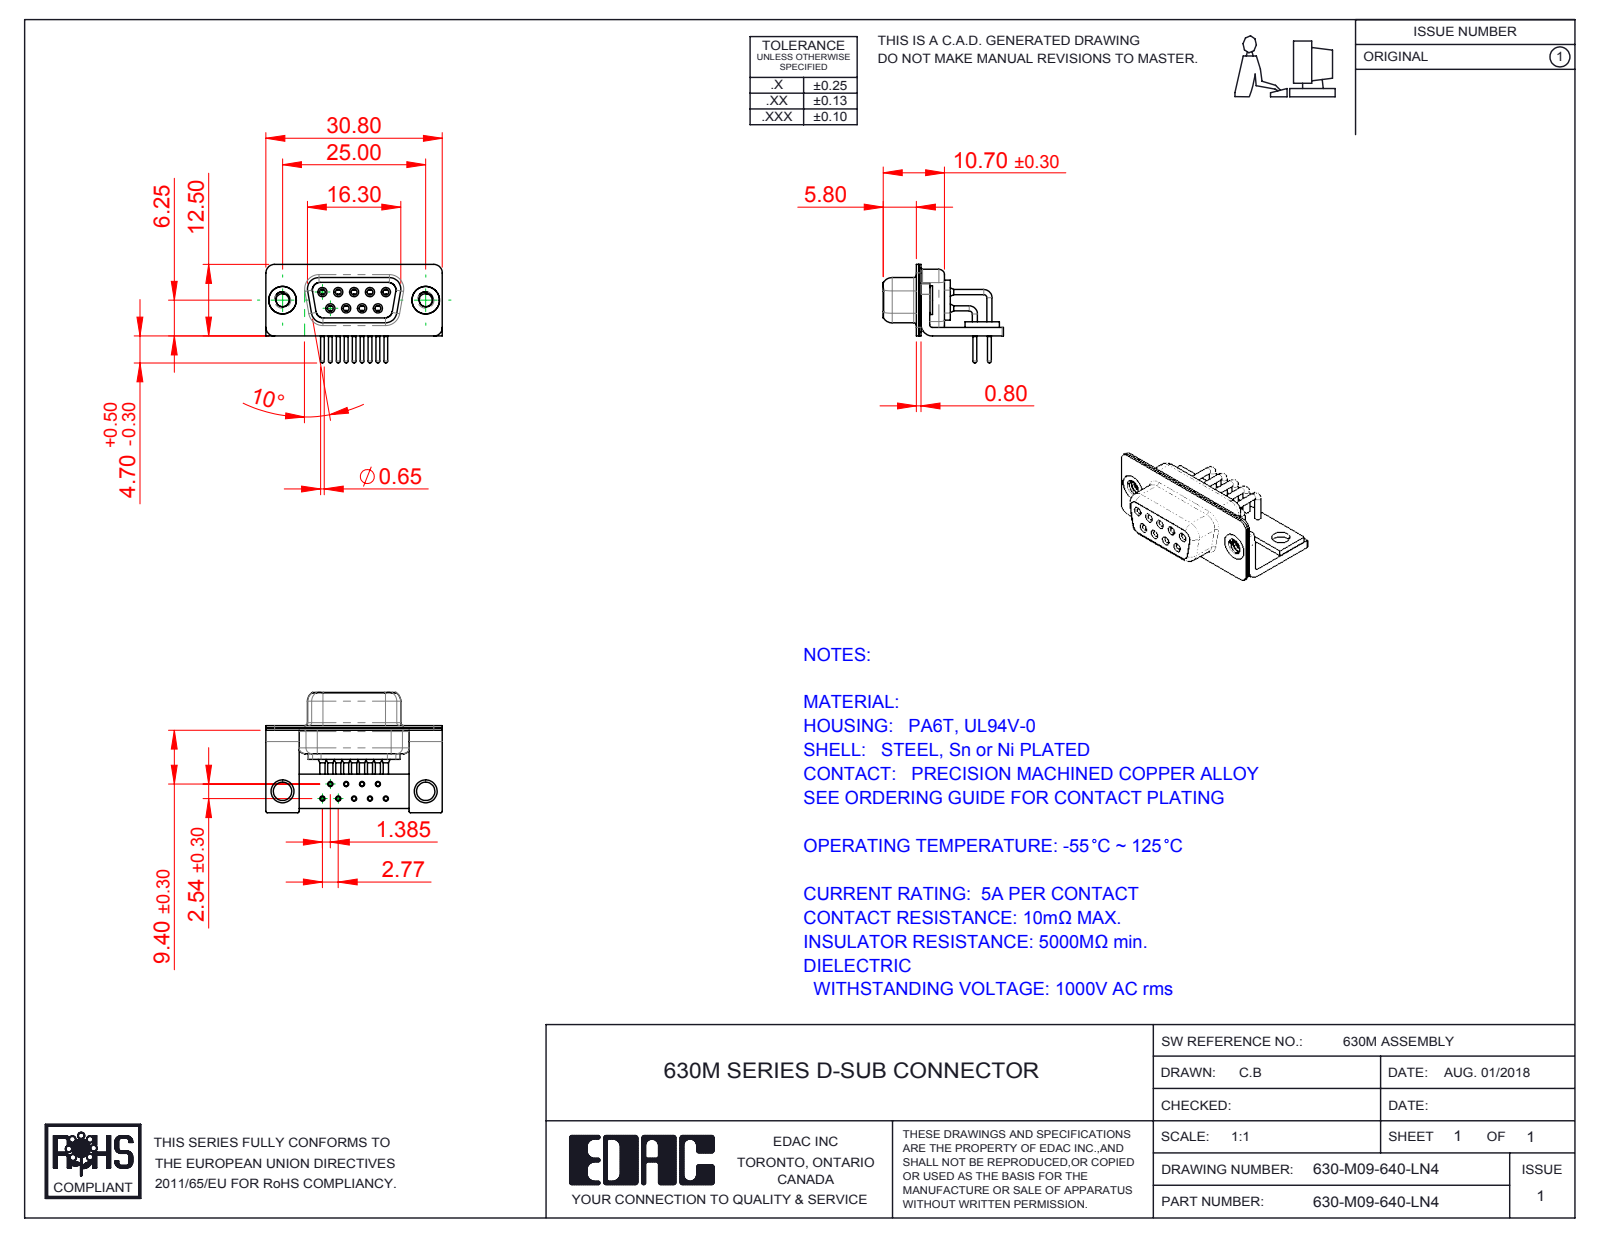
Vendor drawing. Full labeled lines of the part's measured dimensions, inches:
Part name (STEP PRODUCT): 630M Contact Row 2; 630M 4-40 Threaded Rivet_Stabilizer; 630M Stabilizer Bracket; 630M Stabilizer Board_09 Contacts (+5 more)
STEP written by: SolidWorks 2016 (CONFIG_CONTROL_DESIGN)
Units: inches
Bodies: 17 solids, 824 faces (228 planar, 384 cylindrical, 212 other)
Overall size (bounding box): 1.213 × 0.827 × 0.677
Volume: 0.134 in³ · Surface area: 8.795 in²
Round holes (diameter × count): ⌀0.035 ×9, ⌀0.039 ×9, ⌀0.043 ×9, ⌀0.067 ×9, ⌀0.071 ×9, ⌀0.079 ×9, ⌀0.089 ×2, ⌀0.126 ×2, ⌀0.157 ×2, ⌀0.189 ×2
Round bosses / shafts (diameter × count): ⌀0.063 ×9, ⌀0.059 ×9, ⌀0.035 ×9, ⌀0.026 ×9, ⌀0.197 ×2, ⌀0.193 ×2
Partial cylindrical surfaces — rounded edges, fillets, slot ends (radius × count): R0.01 ×16, R0.059 ×16, R0.079 ×13, R0.053 ×8, R0.063 ×8, R0.02 ×5, R0.024 ×4, R0.026 ×4
Main face-to-face distances: 0.016, 0.031, 0.059, 0.091, 0.075, 0.039, 0.368, 0.057, 0.098, 0.352
Hole centre spacings: 0.109, 0.218, 0.124, 0.192, 0.327, 0.114, 0.114, 0.198
